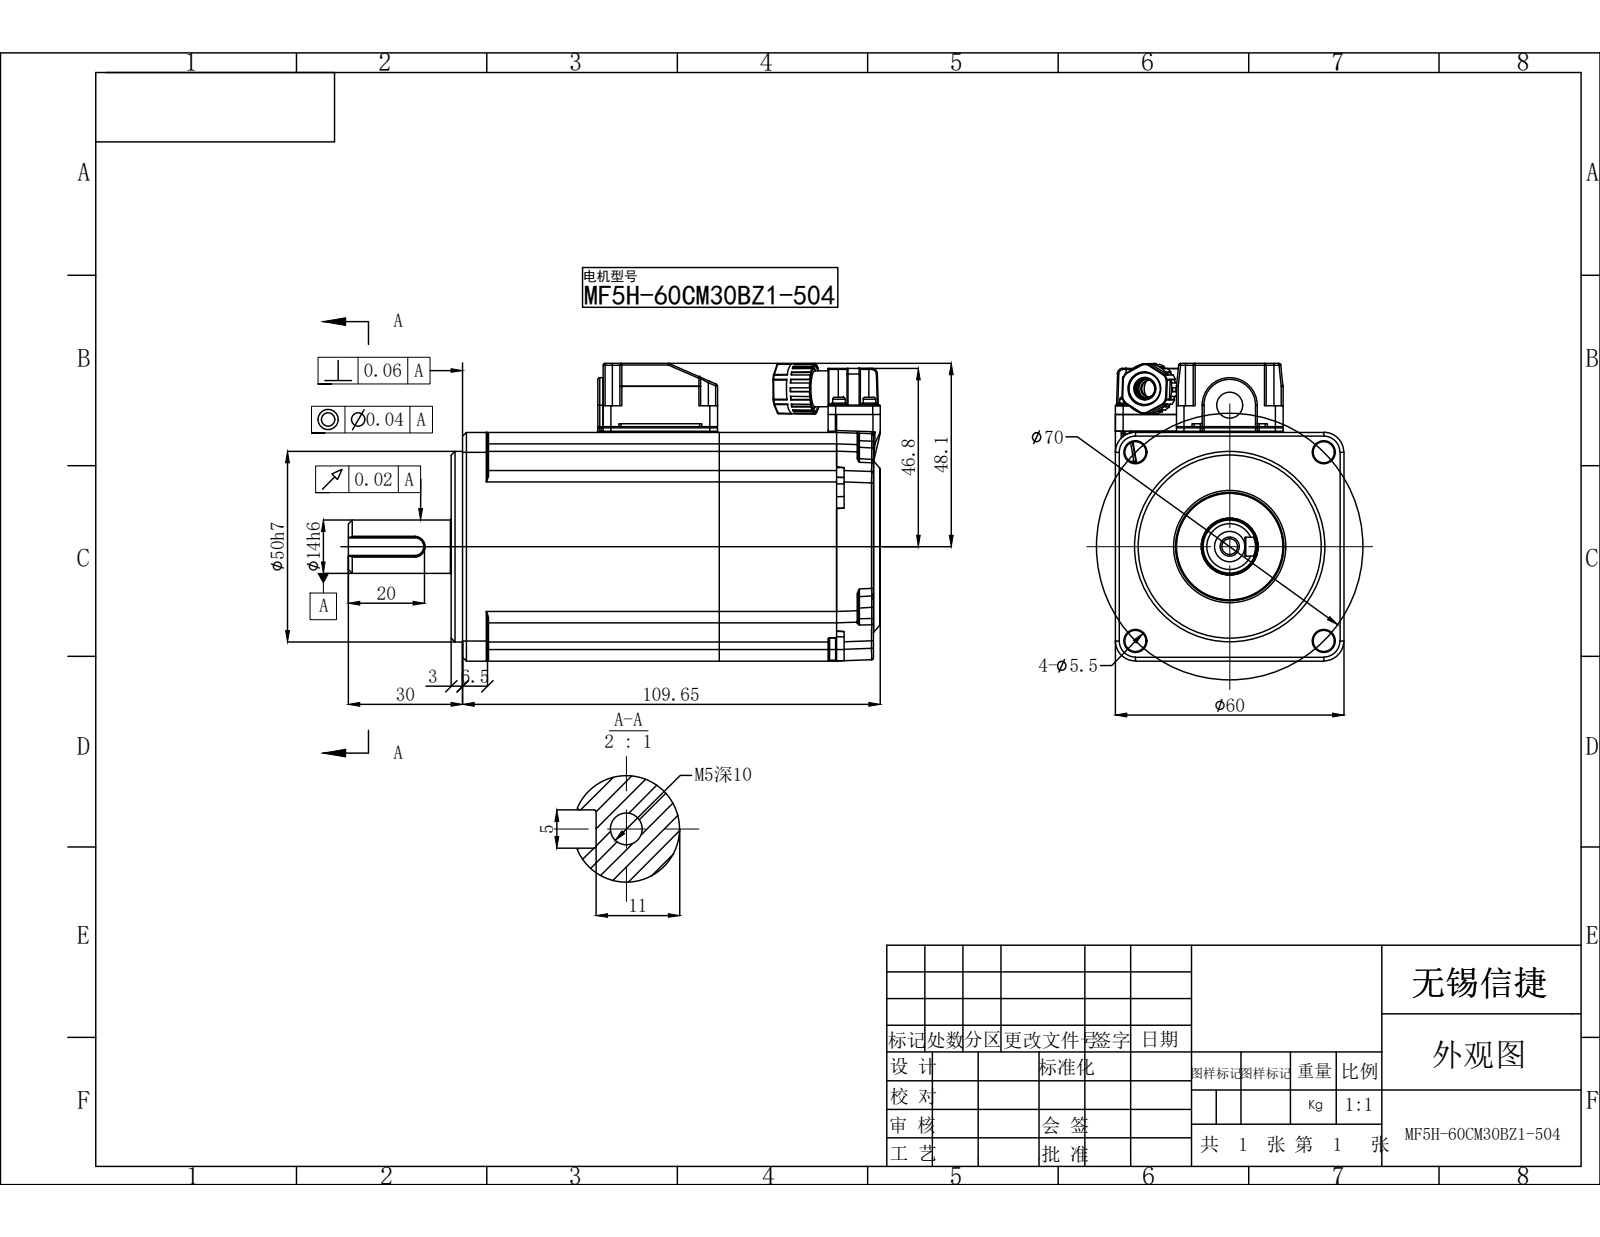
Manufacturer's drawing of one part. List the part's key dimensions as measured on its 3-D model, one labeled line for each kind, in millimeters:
Part name (STEP PRODUCT): MF5H-60CM30BZ1-504
STEP written by: SolidWorks 2016 (CONFIG_CONTROL_DESIGN)
Units: millimetres
Bodies: 0 solids, 928 faces (282 planar, 340 cylindrical, 306 other)
Overall size (bounding box): 139.65 × 78.19 × 60.18
Round holes (diameter × count): ⌀5.5 ×5, ⌀2.3 ×4, ⌀3.5 ×3, ⌀5 ×2, ⌀4.2 ×1, ⌀7.1 ×1, ⌀11.7 ×1, ⌀15 ×1
Round bosses / shafts (diameter × count): ⌀3.9 ×4, ⌀3.3 ×4, ⌀50 ×1, ⌀28 ×1, ⌀14.8 ×1, ⌀14 ×1, ⌀10.4 ×1, ⌀9.4 ×1
Partial cylindrical surfaces — rounded edges, fillets, slot ends (radius × count): R0.5 ×65, R0.3 ×53, R2 ×20, R0.2 ×19, R3 ×18, R5 ×7, R1.5 ×6, R1.09 ×4
Main face-to-face distances: 60, 11.5, 10, 50, 112.65, 101.15, 3, 109.65, 98.15, 1.8
Hole centre spacings: 35, 49.5, 8.55, 31.64, 41.31, 52.4, 66.18, 23.6
